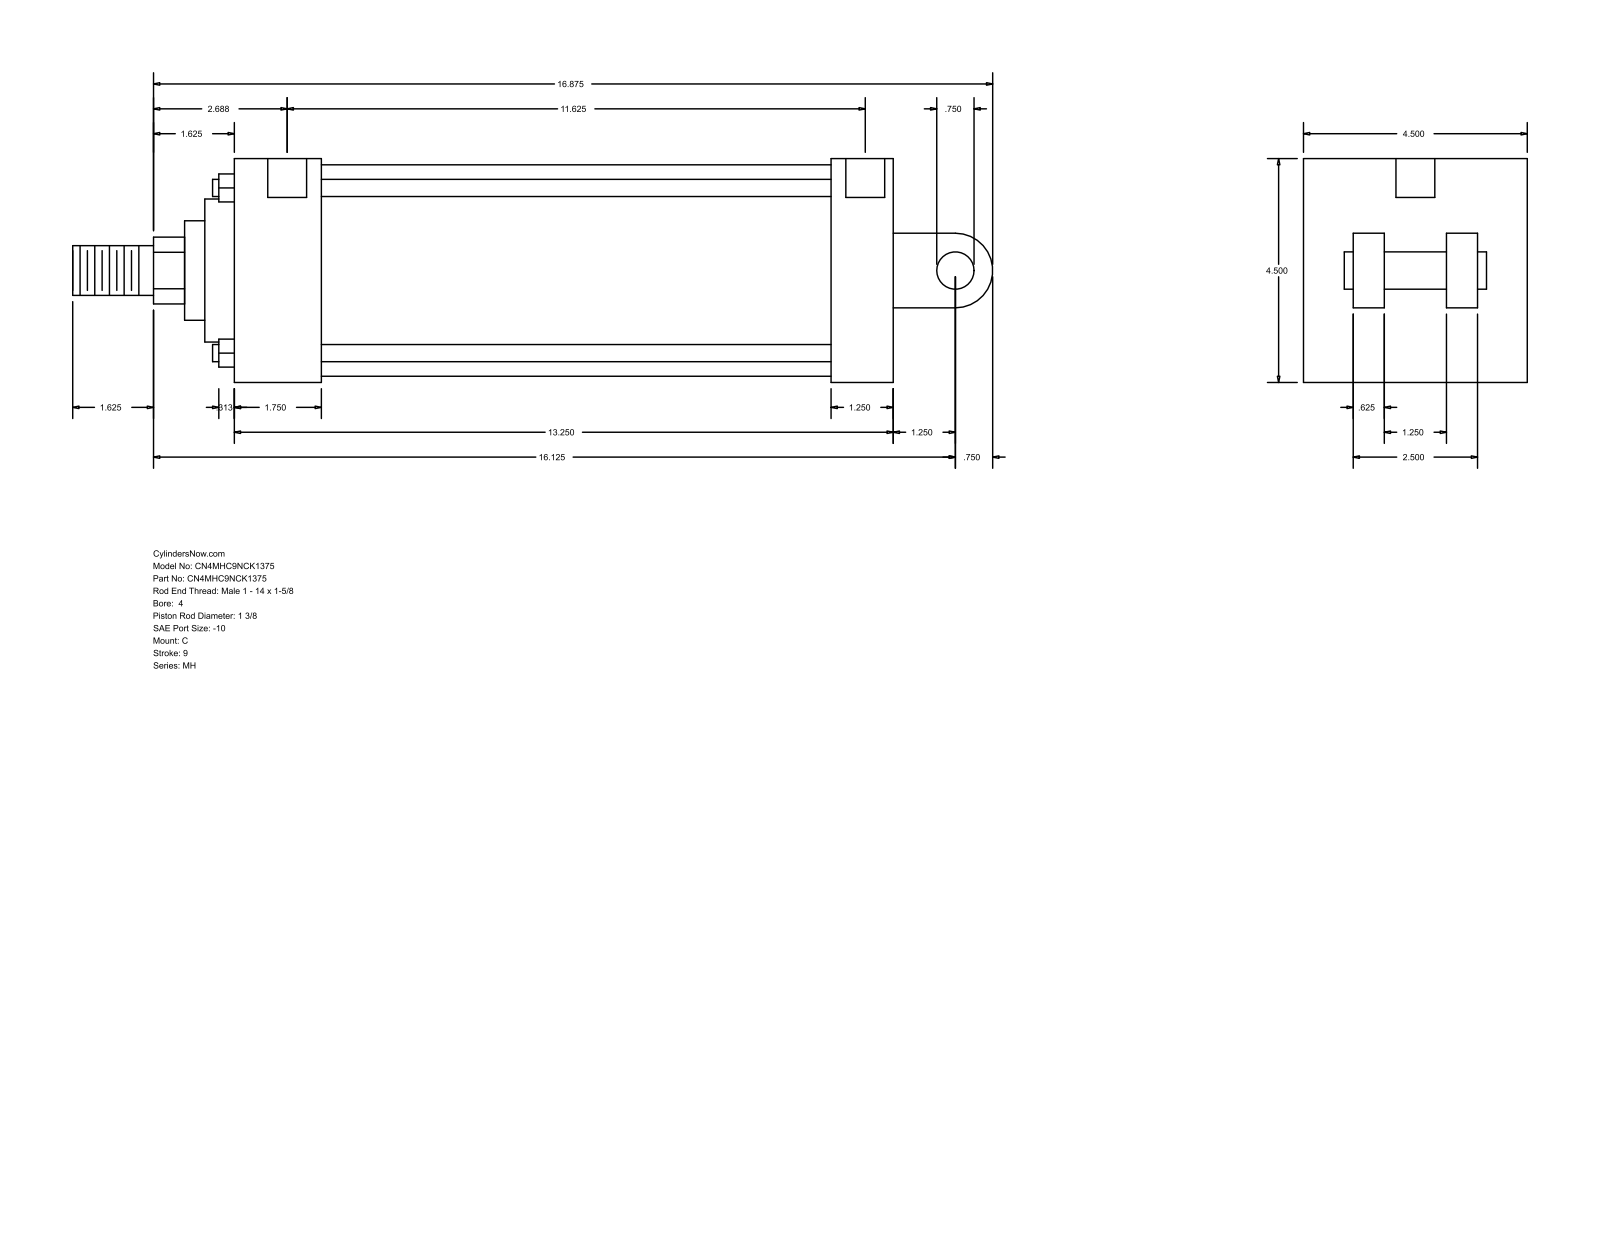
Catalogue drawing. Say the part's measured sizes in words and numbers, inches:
The part is named "MH_C__0400_1.375". Its 3-D file was written by "GSSL Pune (CONFIG_CONTROL_DESIGN)". It is 0 solids with 101 faces: 71 planar, 30 cylindrical and 0 other. Overall it measures 18.5 by 4.5 by 4.5 inches. Round holes: 4 of diameter 0.344, 2 of diameter 0.781. Round bosses or shafts: 4 of diameter 0.345, 1 of diameter 4.25, 1 of diameter 2.875, 1 of diameter 2, 1 of diameter 1.375, 1 of diameter 1, 1 of diameter 0.75. Partial cylindrical surfaces (rounded edges, fillets, slot ends): 1 of radius 0.672, 1 of radius 0.75. The main face-to-face distances are 4.5, 13.25, 1.75, 12, 10.25, 11.5, 1.25, 1.625, 2.875, 1.5. The hole center spacings are 11.75, 0.062, 0.063, 11.625, 11.687, 11.688.
